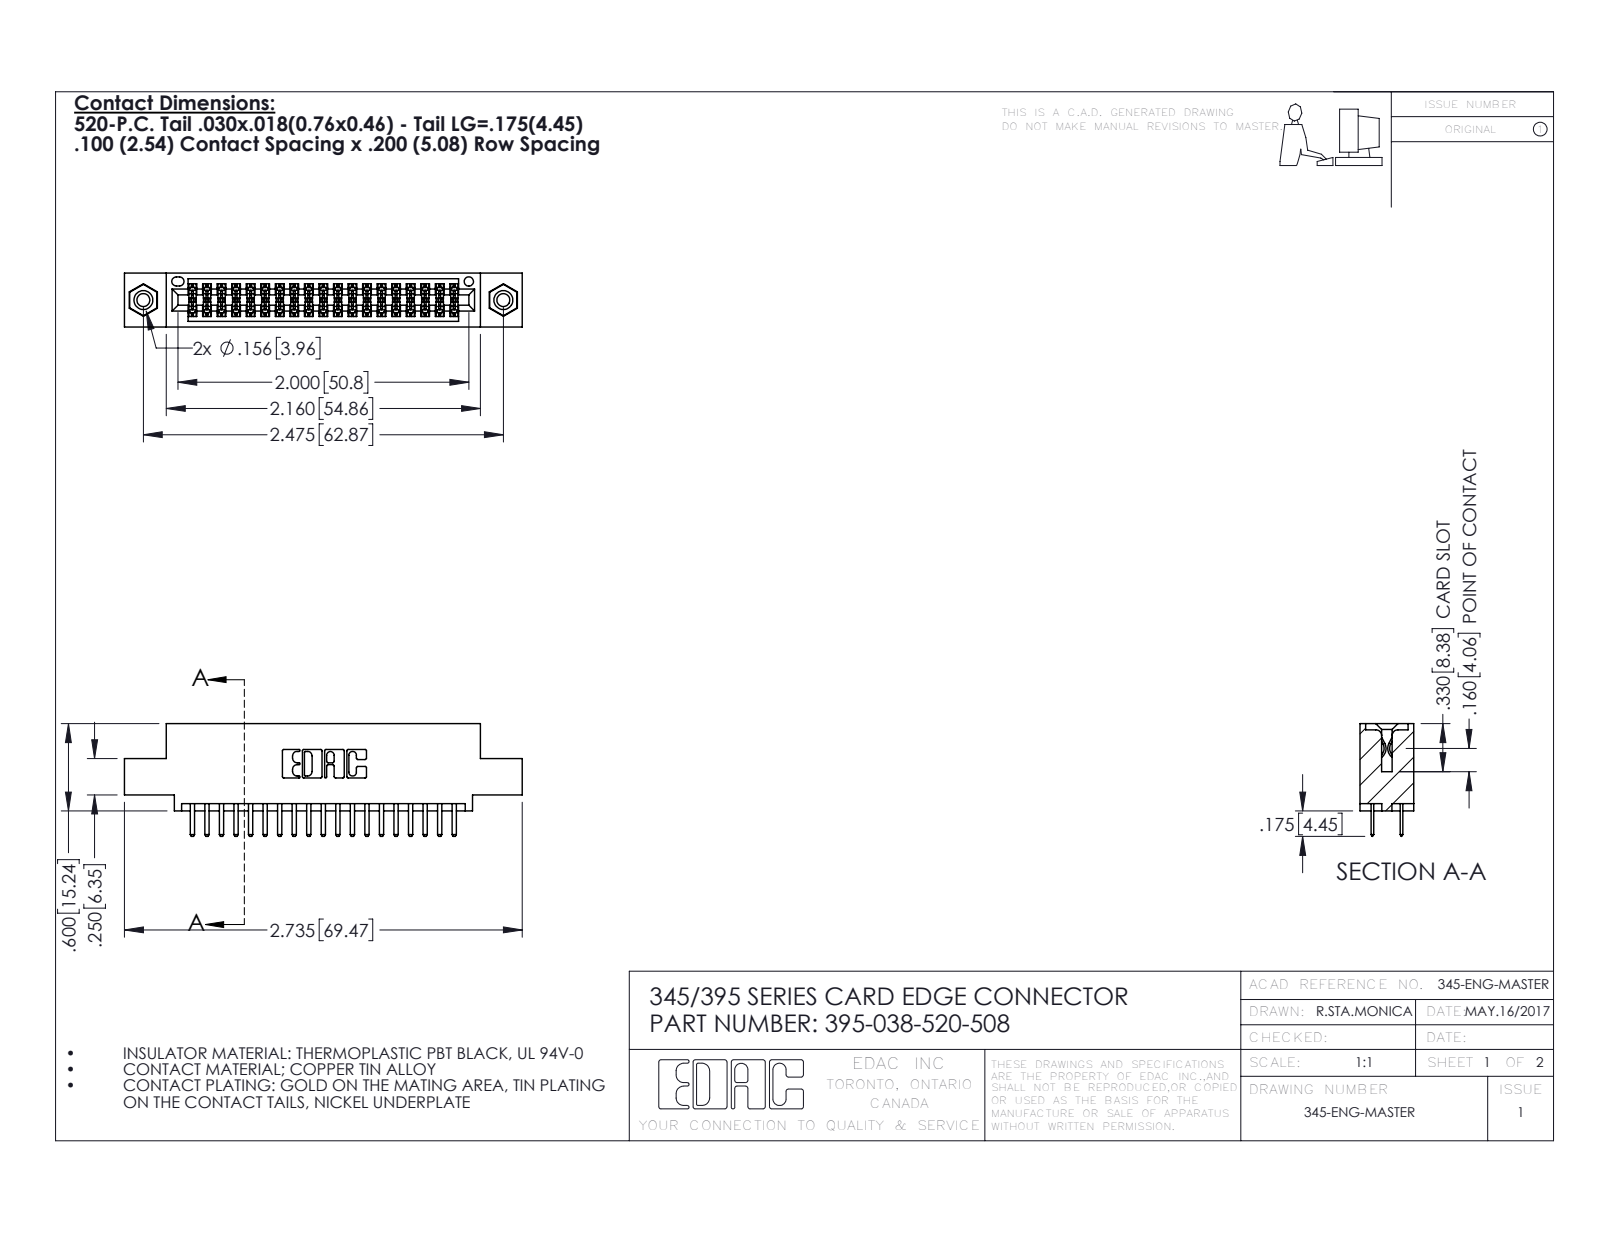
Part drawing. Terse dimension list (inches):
name: 395-038-520-508; 345-292-001_345-293-120; 345-250-001_345-250-003-102; 345 Part_0.110 Offset - 0.156 Dia-TI
written by: SolidWorks 2016 (CONFIG_CONTROL_DESIGN)
unit: in
bodies: 41 solids, 2242 faces (1446 planar, 780 cylindrical, 16 other)
size: 2.735 × 0.775 × 0.37
volume: 0.393 in³; area: 14.17 in²
holes: 2× ⌀0.089, 2× ⌀0.125, 2× ⌀0.156, 1× ⌀0.064
bosses: 2× ⌀0.155
rounds: 57× R0.006, 42× R0.01, 22× R0.01, 6× R0.007, 6× R0.031, 3× R0.026, 2× R0.014, 2× R0.019
face distances: 0.072, 0.298, 0.2, 0.37, 0.098, 0.272, 0.025, 0.225, 0.022, 0.072
hole spacings: 0.27, 2.241, 2.475
